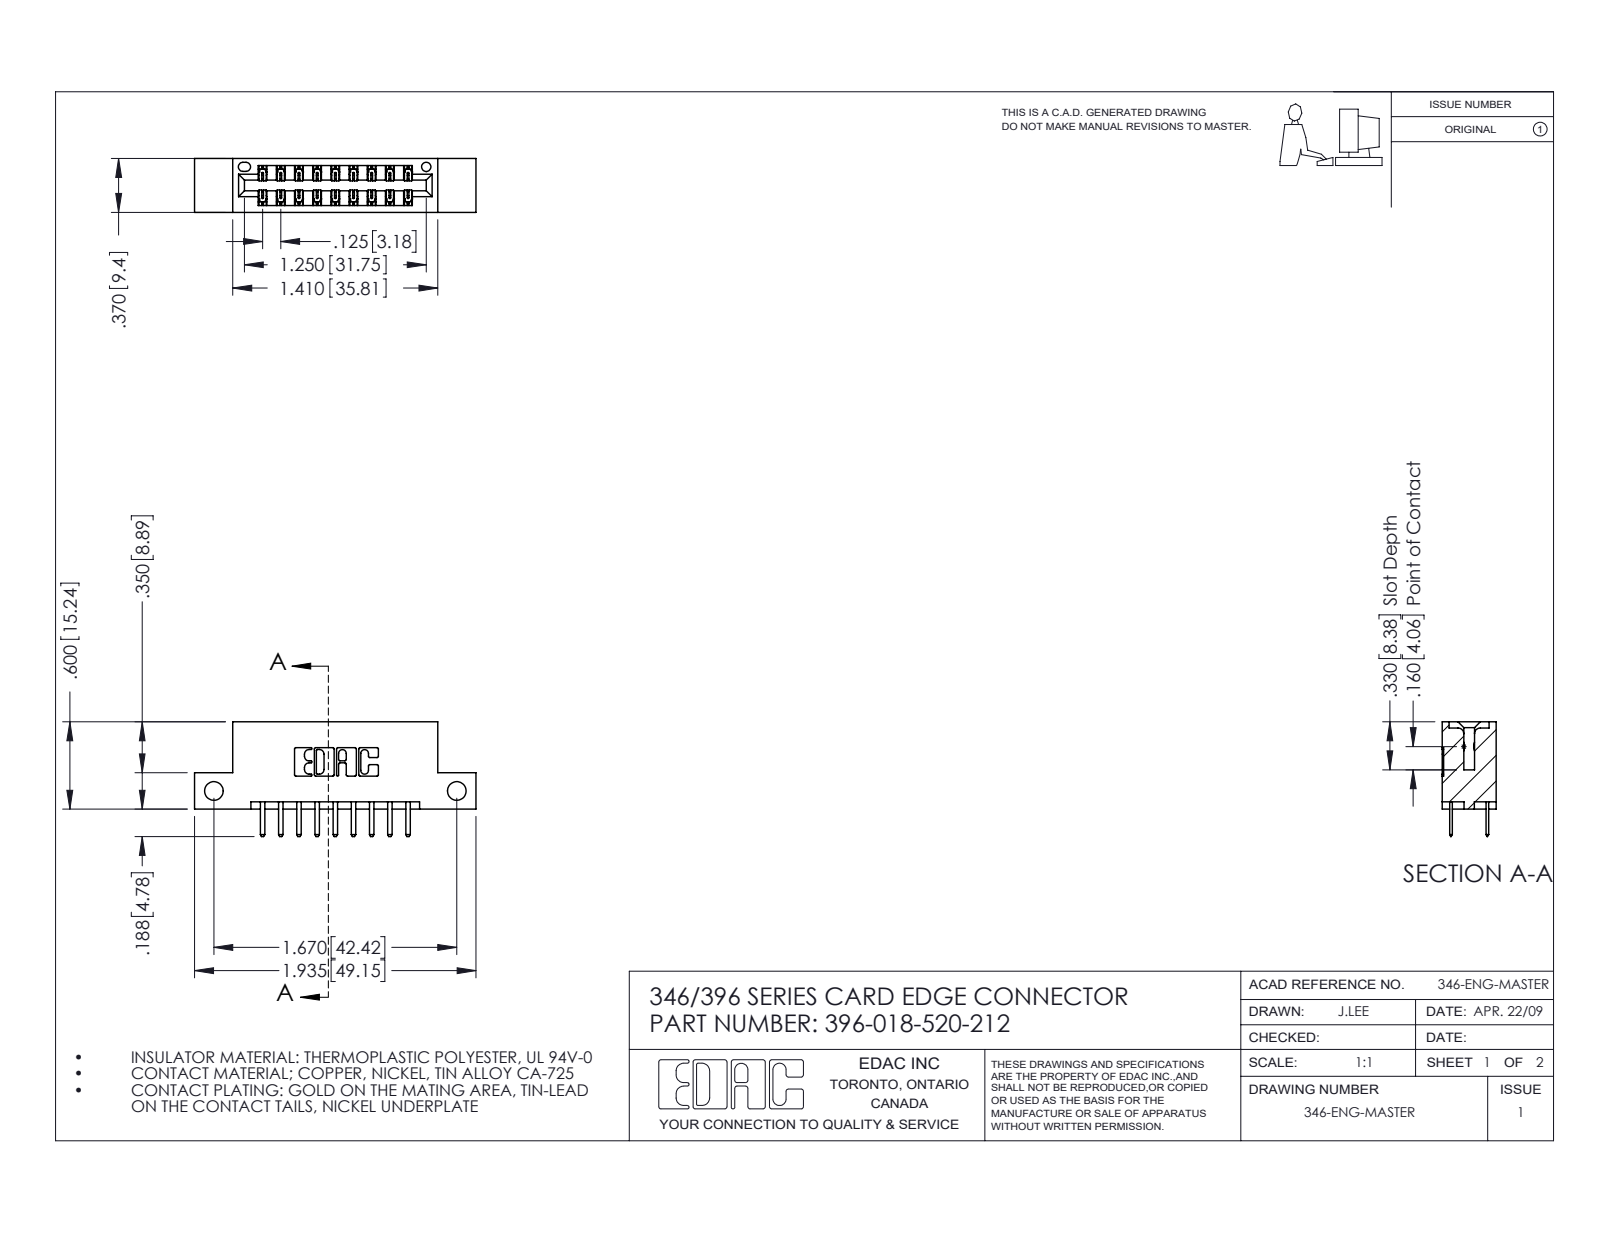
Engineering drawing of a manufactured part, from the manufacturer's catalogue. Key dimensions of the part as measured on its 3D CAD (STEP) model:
Part name (STEP PRODUCT): 345-292-001_345-293-120; 396-018-520-212; 346 Part_Flush Mounting Lugs - Side Mount
STEP written by: SolidWorks 2016 (CONFIG_CONTROL_DESIGN)
Units: inches
Bodies: 19 solids, 1130 faces (742 planar, 388 cylindrical, 0 other)
Overall size (bounding box): 1.935 × 0.788 × 0.37
Volume: 0.271 in³ · Surface area: 8.417 in²
Round holes (diameter × count): ⌀0.128 ×2, ⌀0.064 ×1
Partial cylindrical surfaces — rounded edges, fillets, slot ends (radius × count): R0.006 ×27, R0.01 ×22, R0.01 ×22, R0.007 ×6, R0.031 ×6, R0.026 ×3, R0.014 ×2, R0.022 ×2
Main face-to-face distances: 0.25, 0.048, 0.322, 0.37, 0.148, 0.222, 0.1, 0.174, 0.275, 0.072
Hole centre spacings: 1.67
